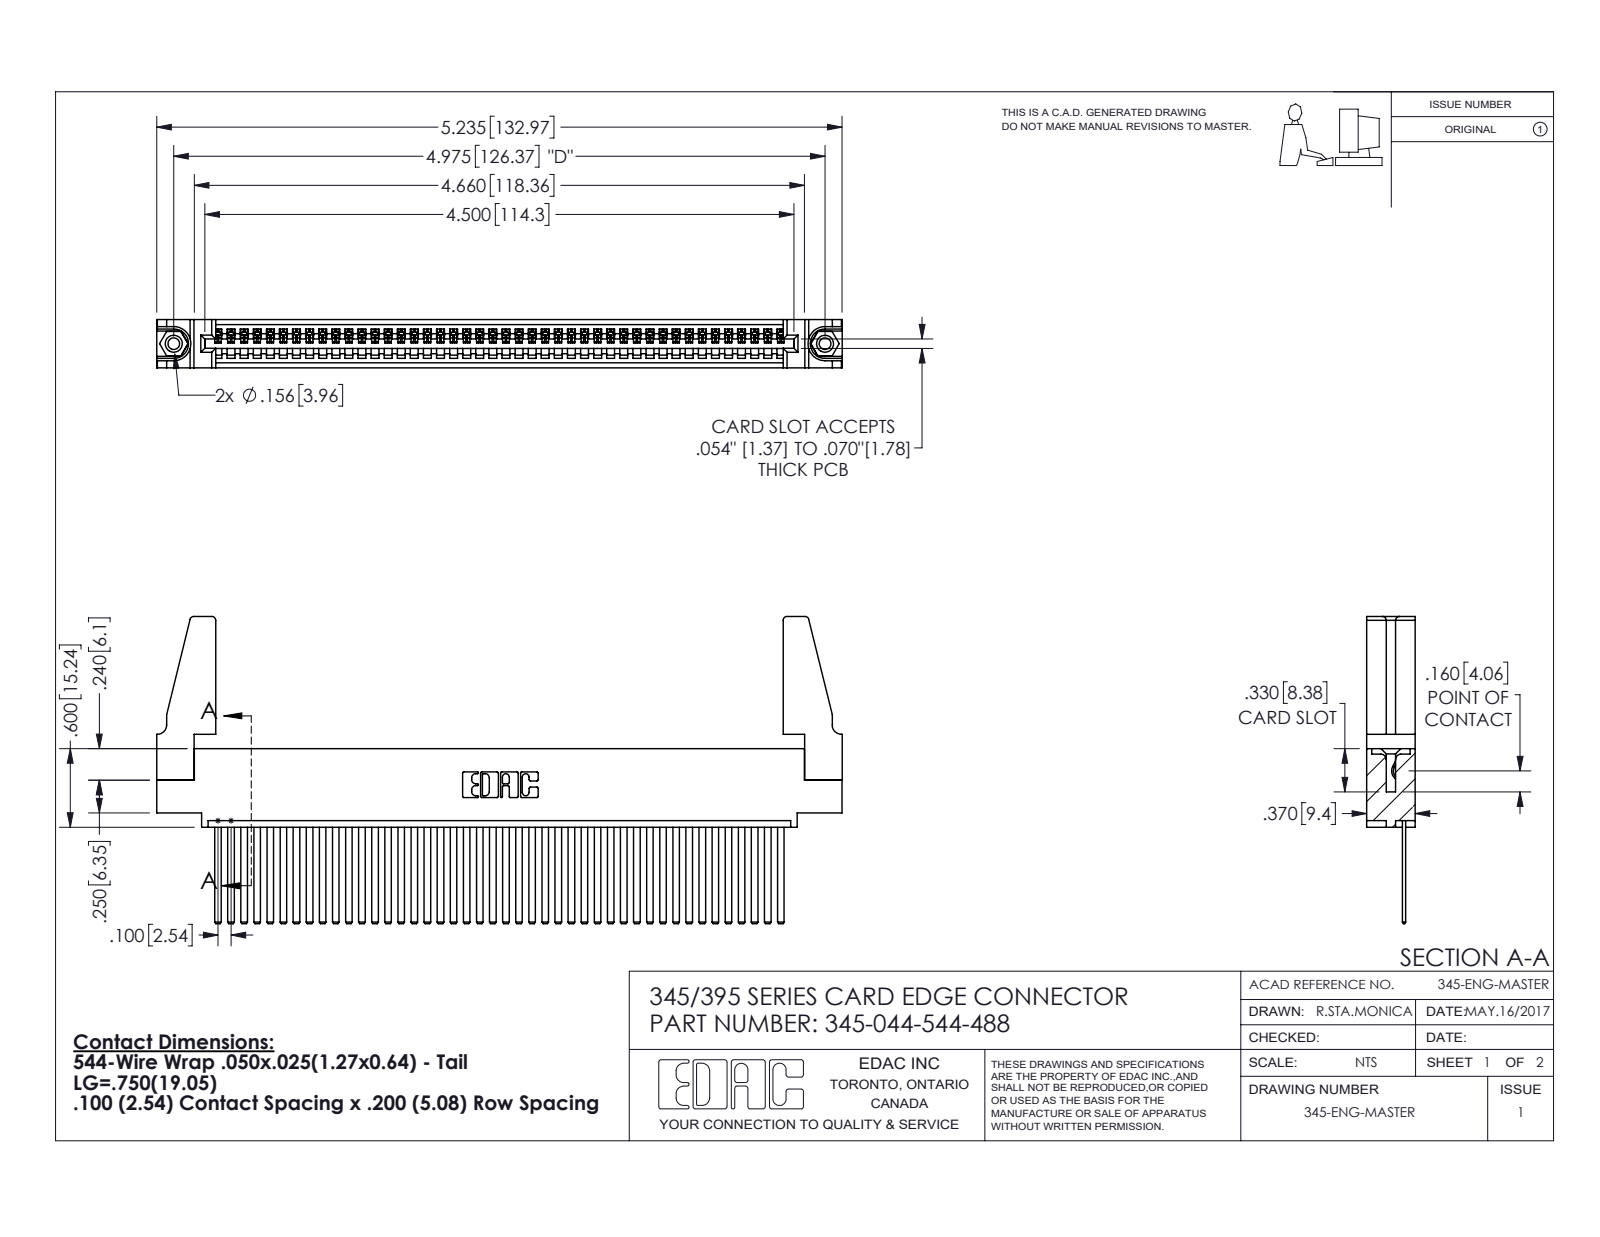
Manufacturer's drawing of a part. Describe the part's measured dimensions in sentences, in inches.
The part is named "345-044-544-488; 345-220-078_345-220-088; 345-292-001_345-293-144; 345-250-001_345-250-001-102 (+1 more)". Its 3-D file was written by "SolidWorks 2016 (CONFIG_CONTROL_DESIGN)". It is 49 solids with 2542 faces: 1740 planar, 786 cylindrical and 16 other. Overall it measures 5.236 by 2.347 by 0.37 inches. Its volume is 0.997 cubic inches and its surface area 34.34 square inches. Round holes: 2 of diameter 0.089, 2 of diameter 0.125, 2 of diameter 0.156, 1 of diameter 0.064. Round bosses or shafts: 2 of diameter 0.155. Partial cylindrical surfaces (rounded edges, fillets, slot ends): 88 of radius 0.006, 22 of radius 0.01, 8 of radius 0.03, 6 of radius 0.007, 6 of radius 0.031, 3 of radius 0.026, 2 of radius 0.031, 2 of radius 0.04. The main face-to-face distances are 0.072, 0.298, 0.098, 0.272, 0.025, 0.37, 0.2, 0.225, 0.149, 0.072. The hole center spacings are 0.27, 4.739, 4.975.
